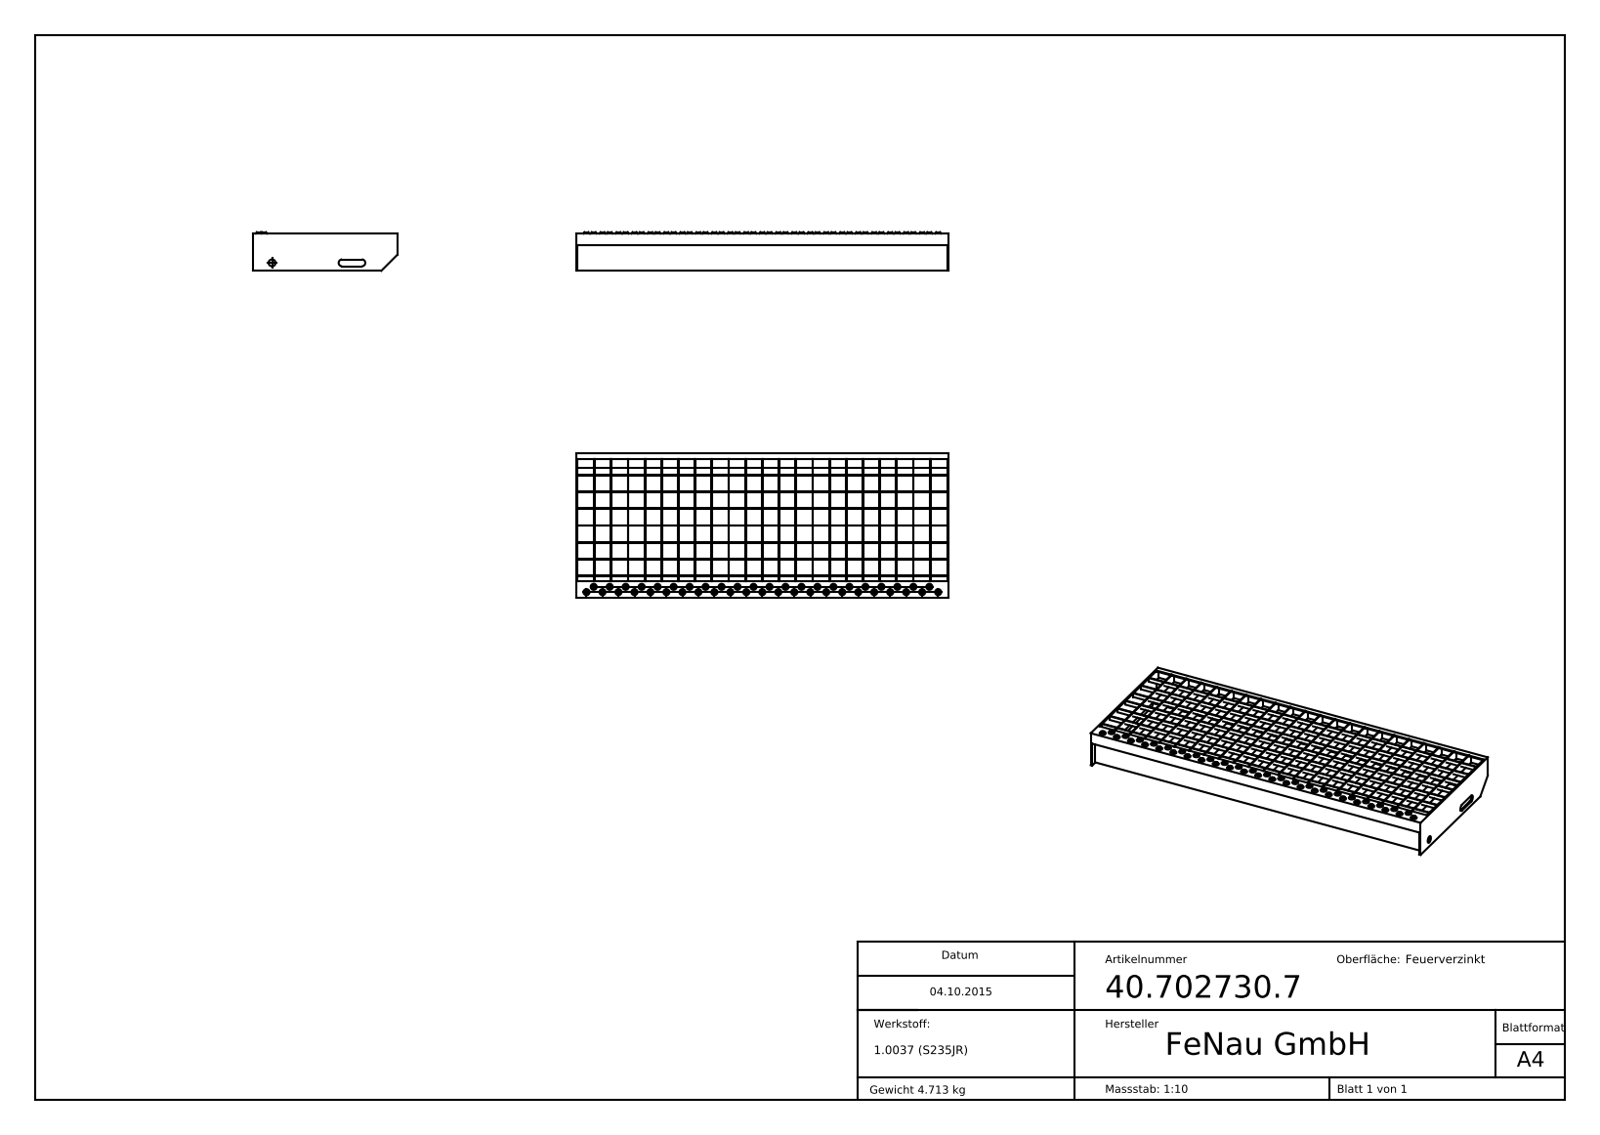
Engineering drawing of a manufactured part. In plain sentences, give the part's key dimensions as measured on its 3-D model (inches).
The part is named "40.702730.7". Its 3-D file was written by "SolidWorks 2015 (CONFIG_CONTROL_DESIGN)". It is 20 solids with 710 faces: 440 planar, 100 cylindrical and 170 other. Overall it measures 27.559 by 10.63 by 2.861 inches. Its volume is 36.87 cubic inches and its surface area 1 063 square inches. Round holes: 45 of diameter 0.276, 1 of diameter 0.512. Partial cylindrical surfaces (rounded edges, fillets, slot ends): 2 of radius 0.256. The main face-to-face distances are 0.079, 1.24, 2.48, 0.059, 3.72, 1.299, 1.181, 2.421, 2.539, 4.961. The hole center spacings are 1.181, 2.362, 3.543, 4.724, 5.906, 7.087, 8.268, 9.449.
